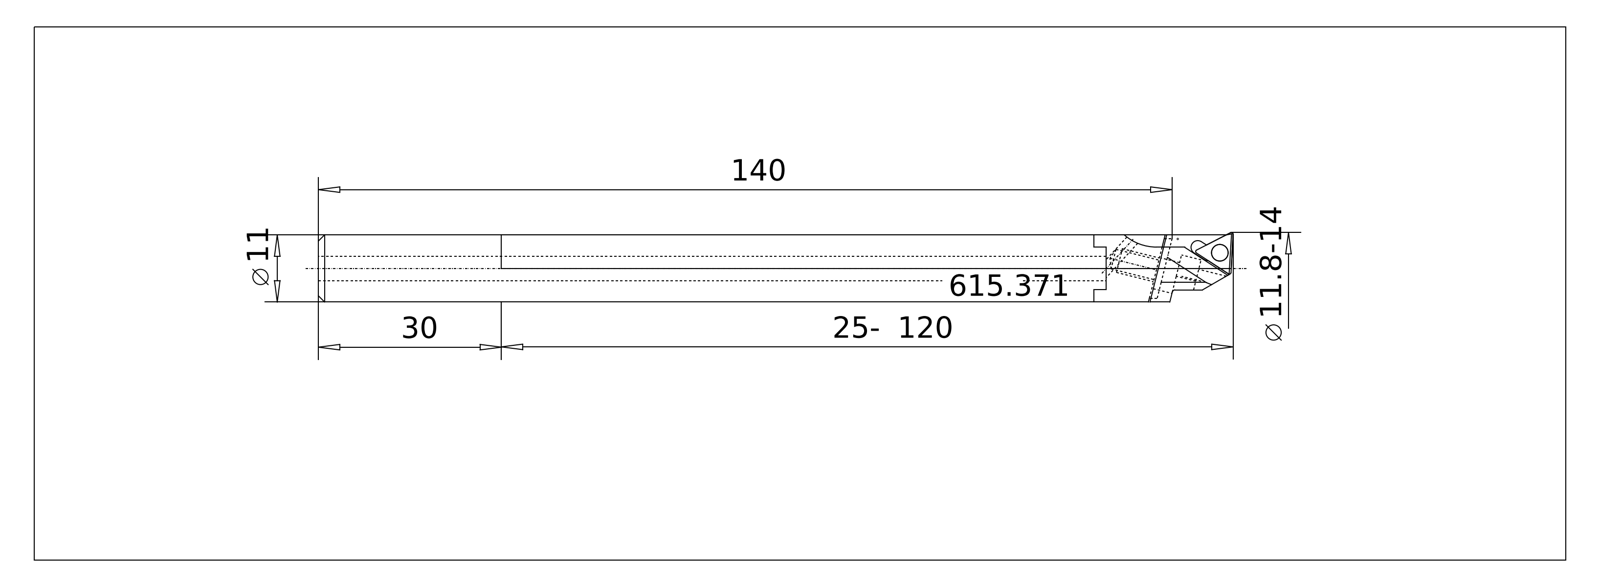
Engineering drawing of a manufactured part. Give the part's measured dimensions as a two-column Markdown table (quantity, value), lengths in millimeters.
| quantity | value |
| --- | --- |
| part name | 615.371 Kaiser VSTH D11 X 140 HM _ D12-14\|615.371 Kaiser VSTH D11 X 140 HM _ D12-14_Standard;NONE; 615.371 Kaiser VSTH D11 X 140 HM _ D12-14\|690.137 Kaiser ETL M4_SW2,5 X 8_Standard;NONE |
| STEP written by | ACIS (automotive_design) |
| units | millimeters |
| bodies | 2 solids, 69 faces (25 planar, 24 cylindrical, 20 other) |
| overall size | 143.66 × 11 × 11 |
| volume | 11 579 mm³ |
| surface area | 6 938 mm² |
| round holes (diameter × count) | 4 × 2, 1.5 × 1, 2 × 1, 3.3 × 1, 4.5 × 1 |
| round bosses / shafts (diameter × count) | 11 × 1, 7.5 × 1, 3.2 × 1 |
| partial cylindrical surfaces (radius × count) | 8 × 1 |
| main face-to-face distances | 1.25, 3.14, 1.89, 2.5, 128.05, 5, 3.94, 2.69, 0.8, 4.86 |
| hole center spacings | 0.4, 4.12, 4.51 |
